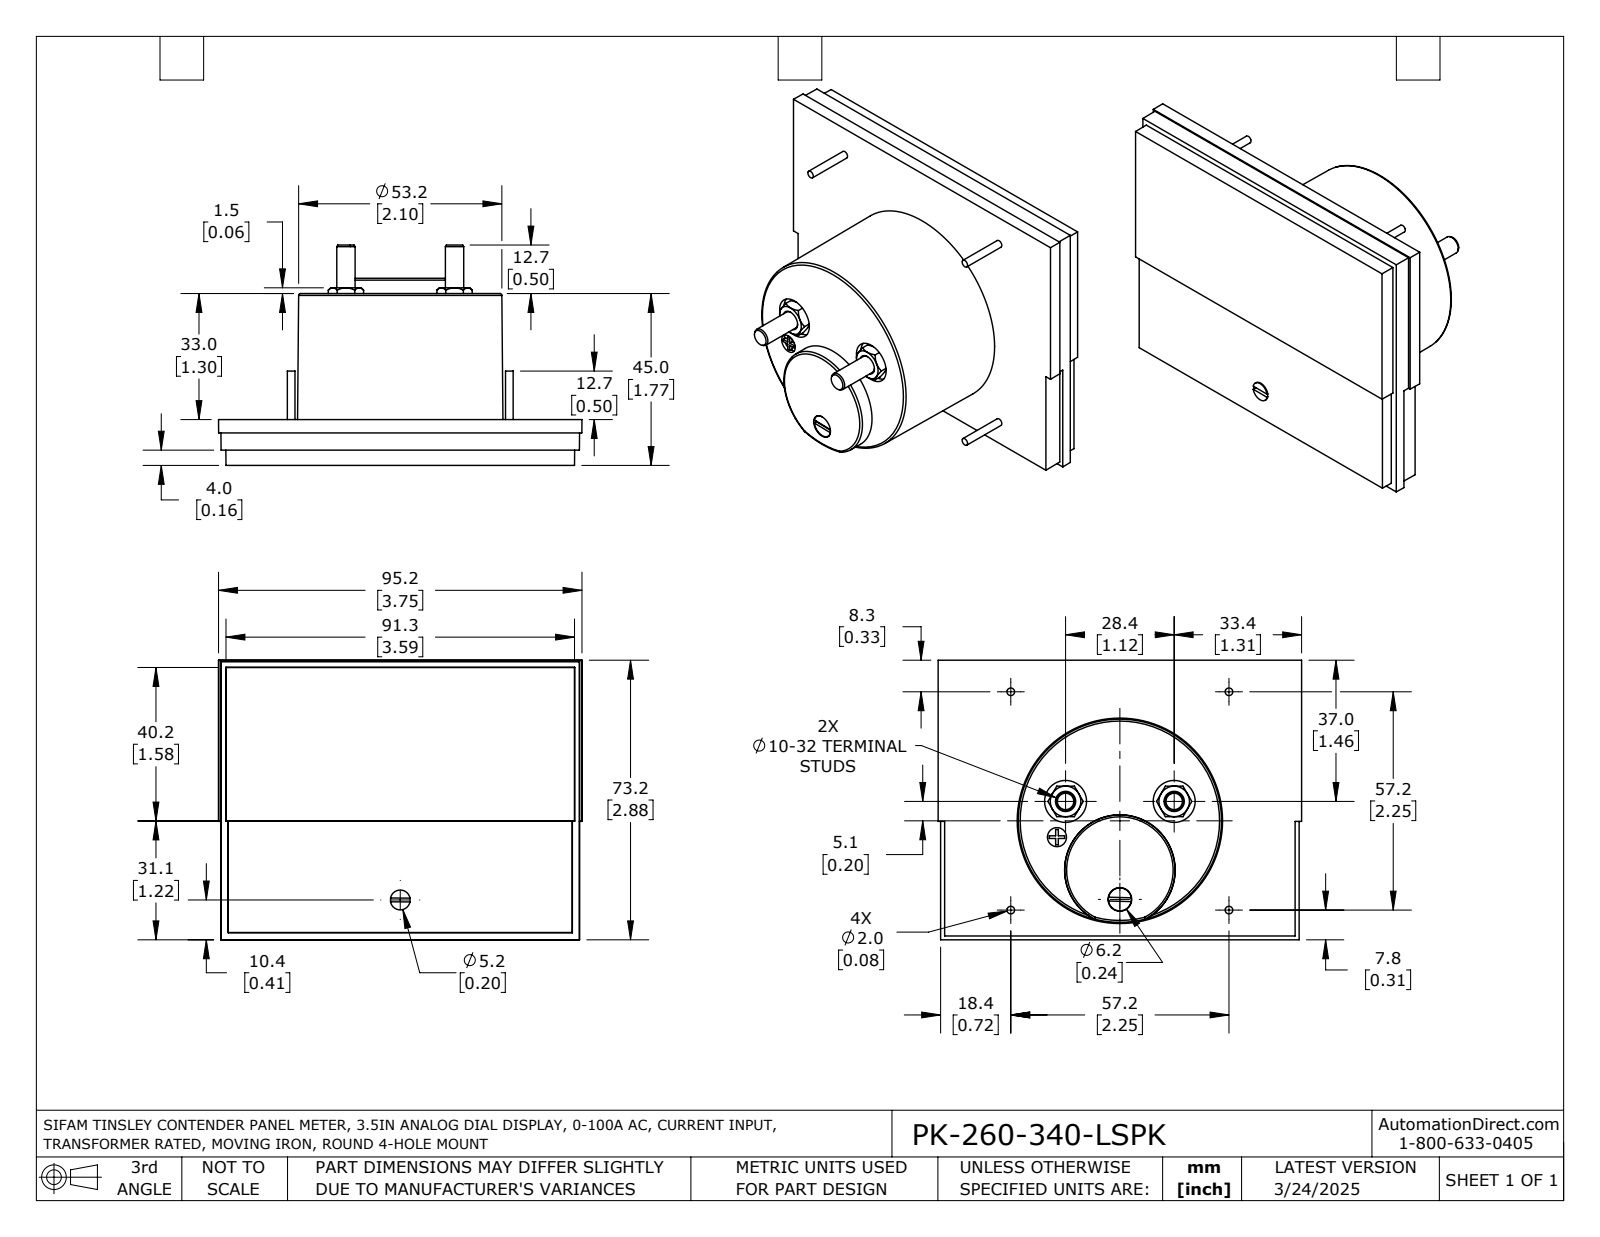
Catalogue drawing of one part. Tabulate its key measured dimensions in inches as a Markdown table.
| quantity | value |
| --- | --- |
| part name | PK-260-340-LSPK |
| STEP written by | SolidWorks 2021 (AUTOMOTIVE_DESIGN) |
| units | inches |
| bodies | 1 solid, 163 faces (76 planar, 31 cylindrical, 56 other) |
| overall size | 3.748 × 2.882 × 2.272 |
| volume | 9.446 in³ |
| surface area | 38.39 in² |
| round holes (diameter × count) | 0.433 × 2, 0.197 × 1, 0.244 × 1 |
| round bosses / shafts (diameter × count) | 0.079 × 4, 0.189 × 2, 0.236 × 1, 0.205 × 1 |
| partial cylindrical surfaces (radius × count) | 0.1 × 1 |
| main face-to-face distances | 0.472, 0.03, 0.443, 1.772, 1.299, 1.742, 0.157, 0.073, 0.315, 1.457 |
| hole center spacings | 1.155, 0.379, 0.912, 1.12, 1.263 |
